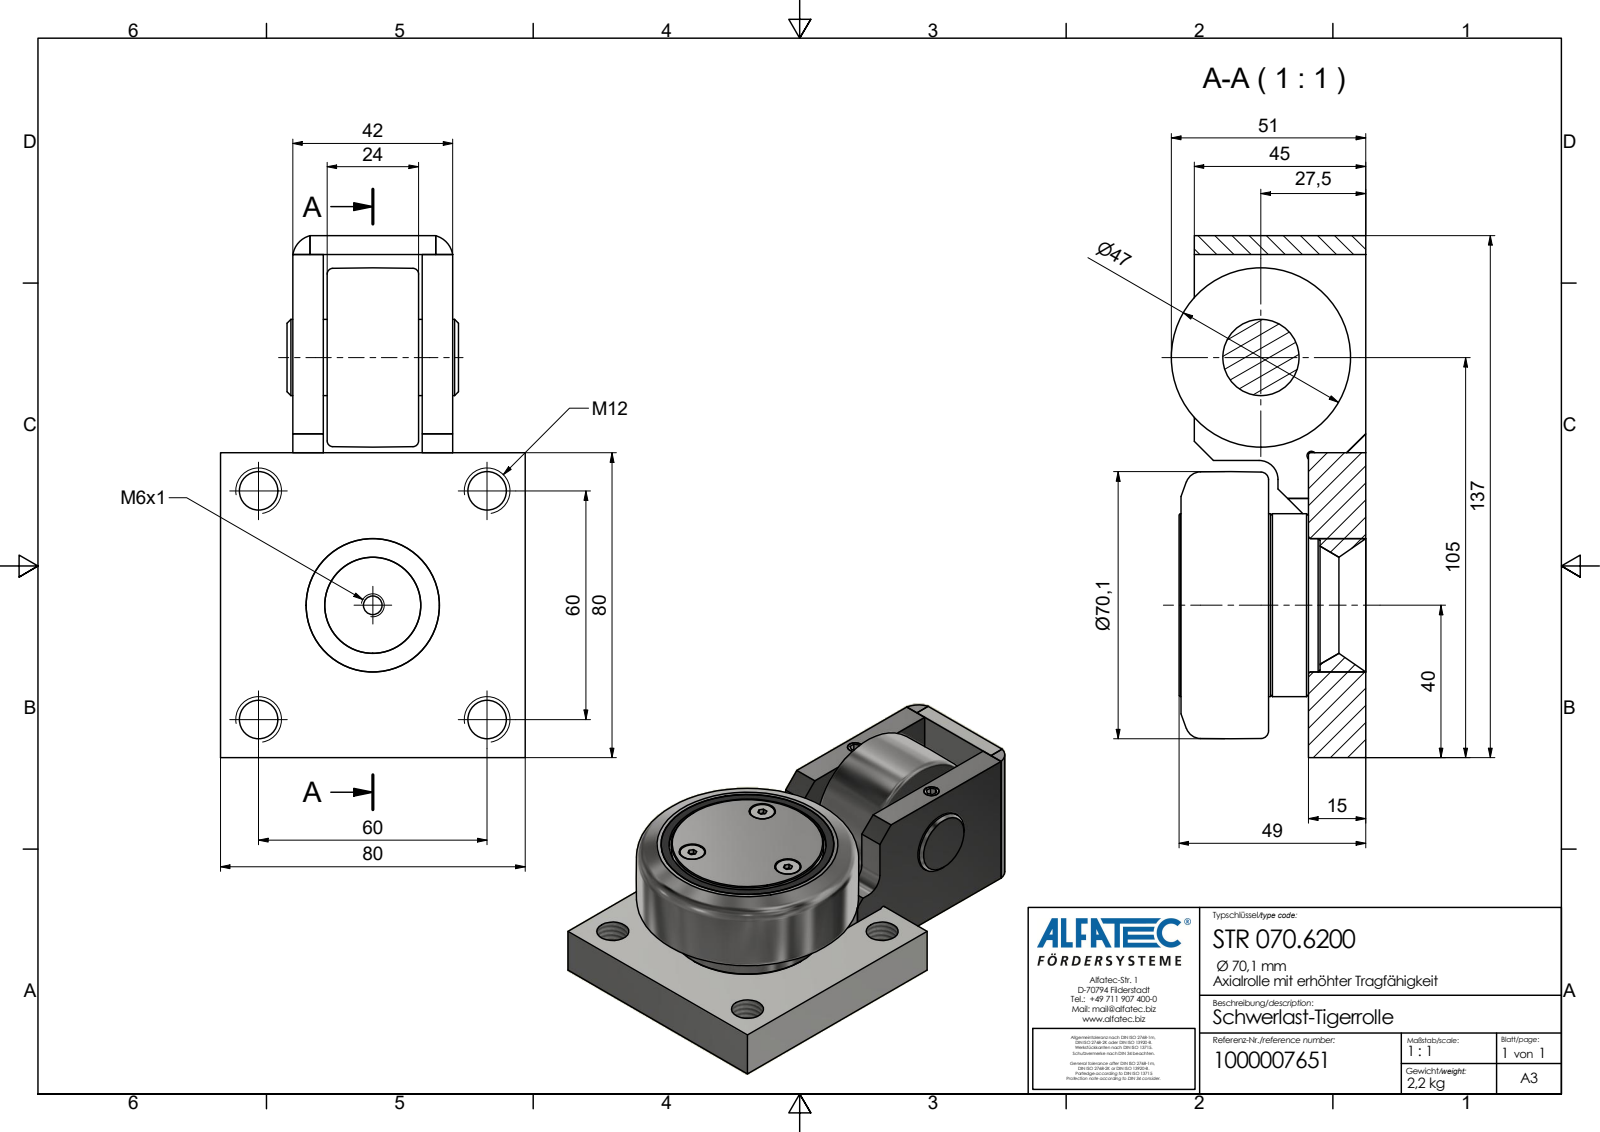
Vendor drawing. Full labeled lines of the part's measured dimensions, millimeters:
Part name (STEP PRODUCT): STR 070.6200_Kontur
STEP written by: Autodesk Inventor 2020 (AP242_MANAGED_MODEL_BASED_3D_ENGINEERING_MIM_LF)
Units: millimetres
Bodies: 2 solids, 129 faces (74 planar, 30 cylindrical, 25 other)
Overall size (bounding box): 137 × 80 × 51
Volume: 282 987 mm³ · Surface area: 53 255 mm²
Round holes (diameter × count): ⌀10.11 ×4, ⌀4.92 ×3, ⌀8.3 ×3, ⌀20.1 ×1
Round bosses / shafts (diameter × count): ⌀7.8 ×3, ⌀48 ×1, ⌀20 ×1
Partial cylindrical surfaces — rounded edges, fillets, slot ends (radius × count): R6.16 ×2, R1.2 ×1, R5 ×1
Main face-to-face distances: 34, 8, 15, 52, 42, 25, 19, 27, 53, 61
Hole centre spacings: 60, 42.43, 18, 31.18, 25.47, 32.31, 37.34, 41.58
